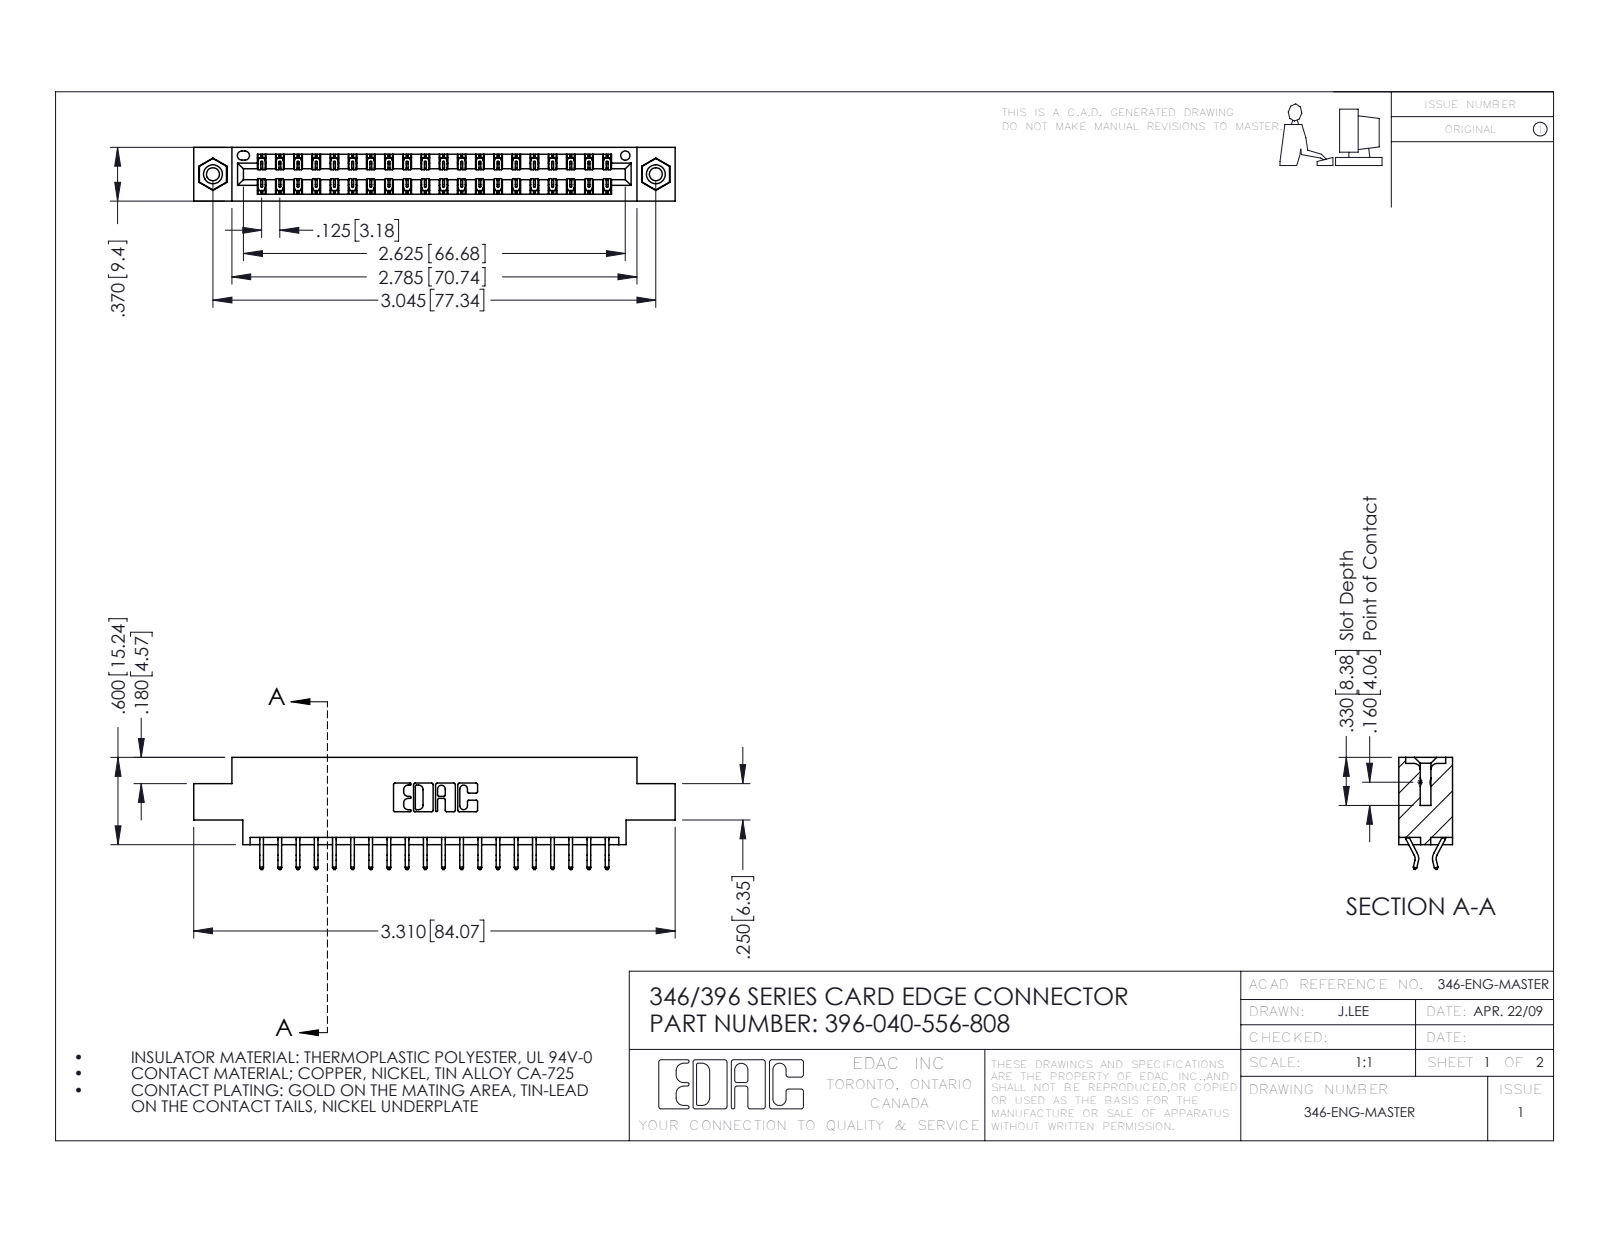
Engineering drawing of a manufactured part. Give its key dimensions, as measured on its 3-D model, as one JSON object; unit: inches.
{"part_name": "396-040-556-808; 345-250-001_345-250-003-102; 345-292-001_556 Tail; 346 Part_0.170 Offset - 0.156 Dia-TI", "step_written_by": "SolidWorks 2016 (CONFIG_CONTROL_DESIGN)", "units": "inches", "bodies": {"solids": 43, "faces": 2506, "planar": 1672, "cylindrical": 818, "other": 16}, "overall_size": [3.31, 0.77, 0.37], "volume_in3": 0.48, "surface_area_in2": 16.47, "round_holes": [[0.089, 2], [0.125, 2], [0.156, 2], [0.064, 1]], "round_bosses_or_shafts": [[0.155, 2]], "partial_cylinders_radius": [[0.006, 60], [0.01, 22], [0.007, 6], [0.031, 6], [0.026, 3], [0.01, 2], [0.014, 2], [0.022, 2]], "face_to_face_distances": [0.048, 0.322, 0.37, 0.25, 0.025, 0.072, 0.298, 0.275, 0.222, 0.148], "hole_center_spacings": [0.246, 2.837, 3.045]}
